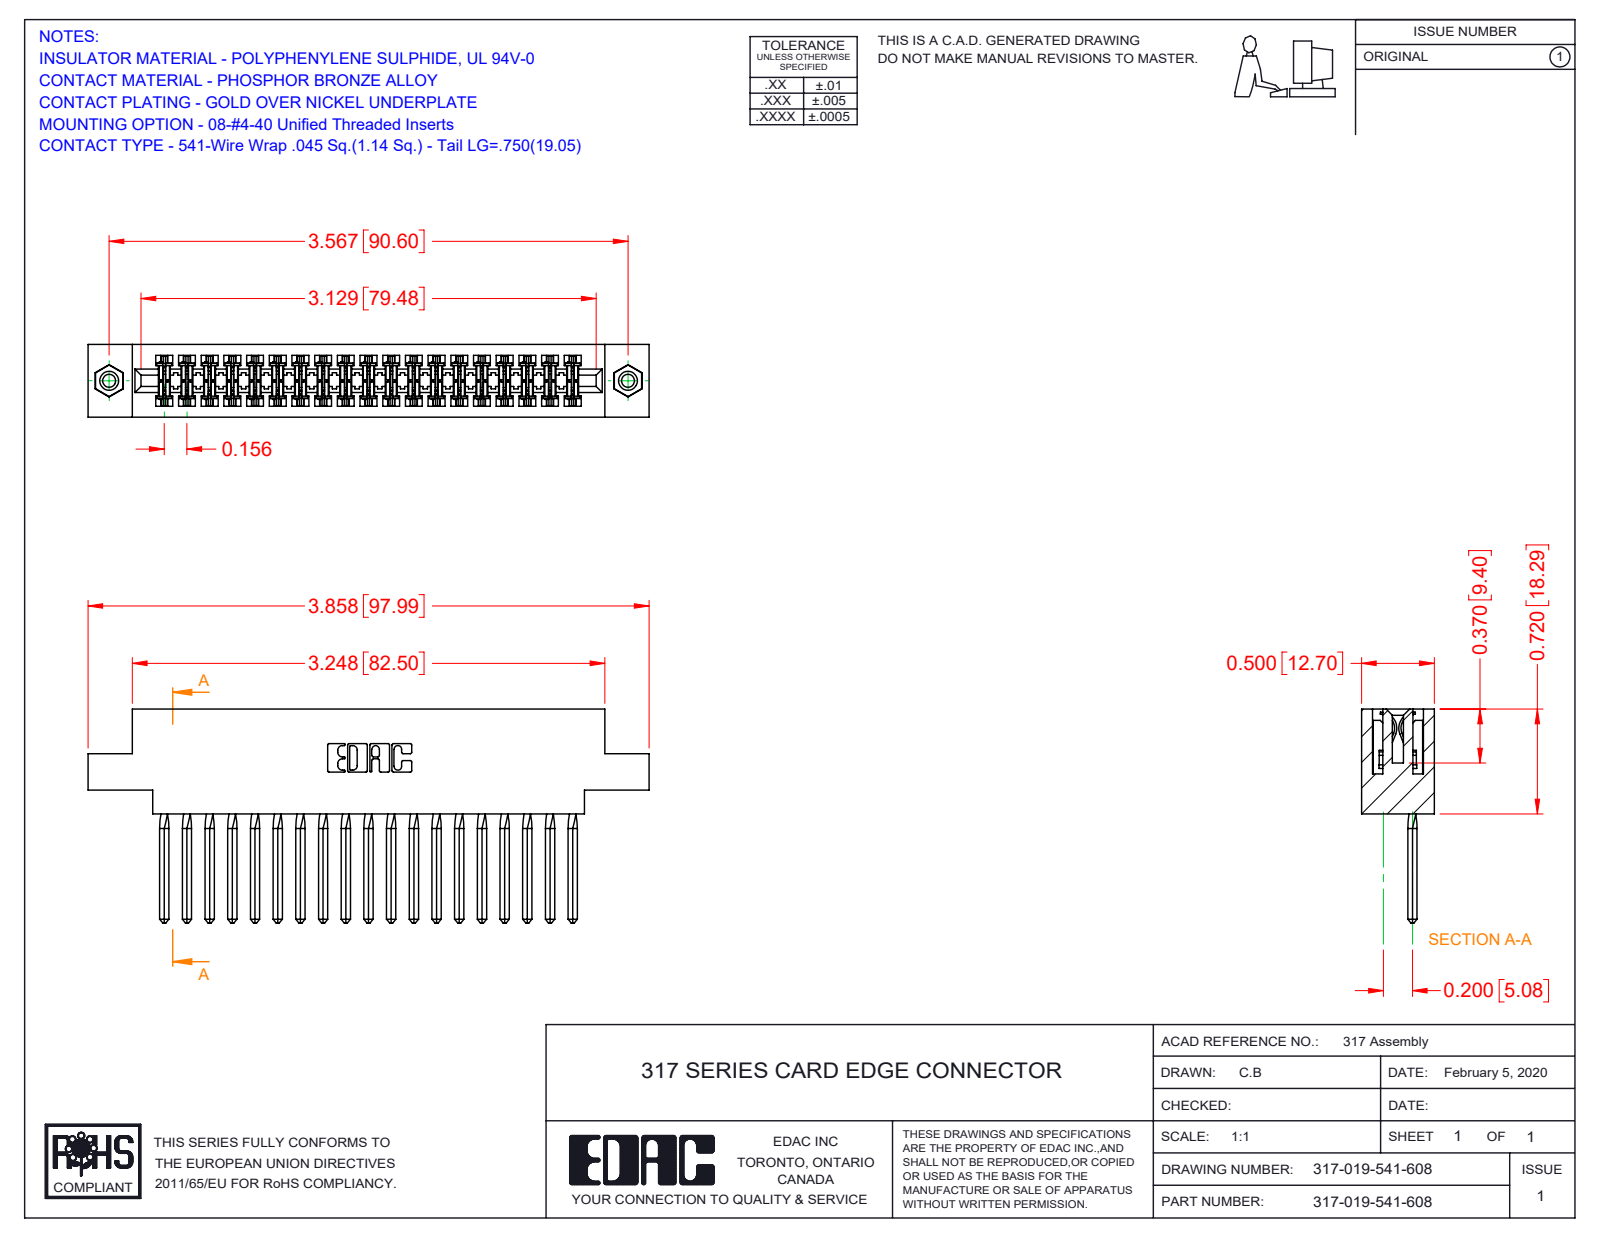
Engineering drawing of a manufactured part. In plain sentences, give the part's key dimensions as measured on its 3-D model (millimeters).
The part is named "345-250-001_345-250-003-102; 317 Part_.156 Dia - TI; 317-290-002_541; 317-019-541-608". Its 3-D file was written by "SolidWorks 2016 (CONFIG_CONTROL_DESIGN)". It is 22 solids with 3050 faces: 2446 planar, 512 cylindrical and 92 other. Overall it measures 98 by 37.3 by 12.7 millimeters. Its volume is 15 200 cubic millimeters and its surface area 20 700 square millimeters. Round holes: 2 of diameter 2.3, 2 of diameter 3.2, 2 of diameter 4. Round bosses or shafts: 2 of diameter 3.9. Partial cylindrical surfaces (rounded edges, fillets, slot ends): 38 of radius 0.4, 22 of radius 0.3, 6 of radius 0.2, 6 of radius 0.8, 3 of radius 0.7, 2 of radius 2.4, 2 of radius 2.5, 2 of radius 2.8. The main face-to-face distances are 12.7, 1.9, 10.8, 2.8, 8.9, 5, 19.6, 5.6, 16.8, 18.3. The hole center spacings are 90.6.
